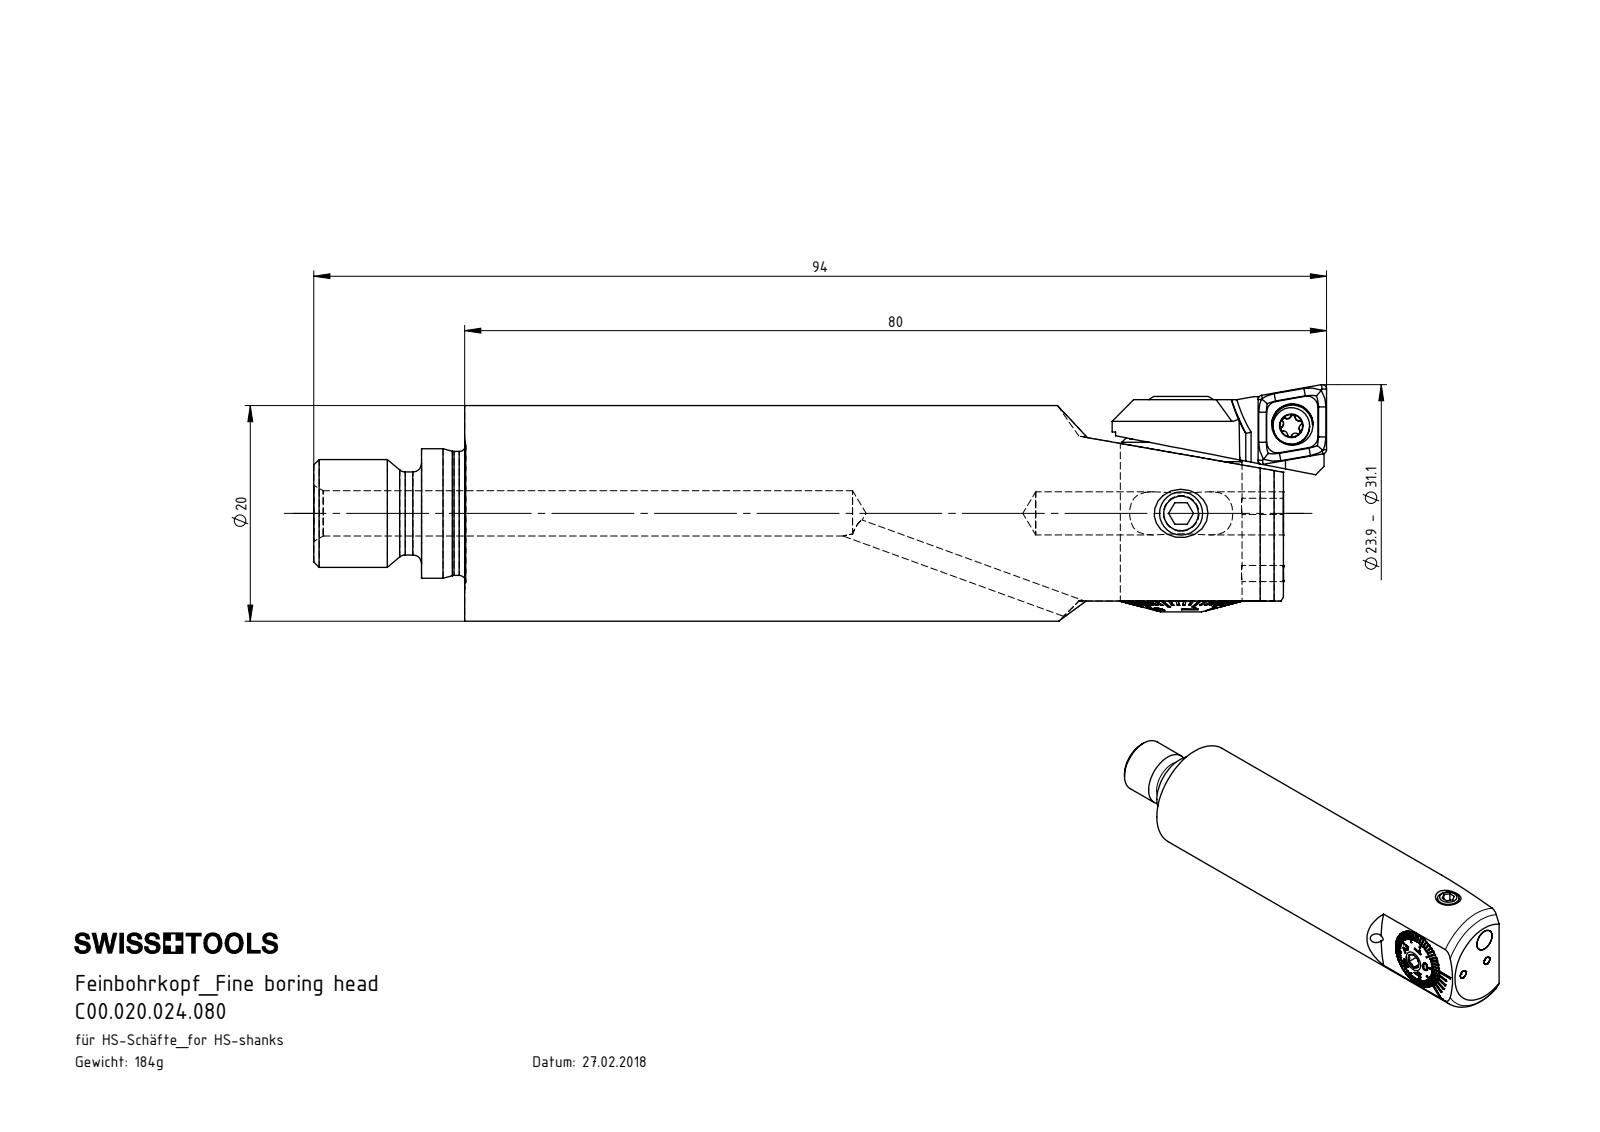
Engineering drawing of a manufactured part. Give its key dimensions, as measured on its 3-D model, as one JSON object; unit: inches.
{"part_name": "ISO 8744-1.5x5; ISO 4026 - M4 x 3; DIN 3771 - 9x1; C00.020.024.080 (+8 more)", "step_written_by": "SolidWorks 2017 (CONFIG_CONTROL_DESIGN)", "units": "inches", "bodies": {"solids": 15, "faces": 756, "planar": 336, "cylindrical": 142, "other": 278}, "overall_size": [3.701, 0.864, 0.787], "volume_in3": 1.433, "surface_area_in2": 15.85, "round_holes": [[0.055, 2], [0.13, 2], [0.02, 1], [0.059, 1], [0.079, 1], [0.081, 1], [0.11, 1], [0.148, 1], [0.152, 1], [0.157, 1], [0.165, 1], [0.177, 1]], "round_bosses_or_shafts": [[0.059, 3], [0.157, 2], [0.787, 1], [0.472, 1], [0.453, 1], [0.445, 1], [0.394, 1], [0.356, 1]], "partial_cylinders_radius": [[0.008, 6], [0.014, 5], [0.012, 2], [0.02, 2], [0.039, 2], [0.197, 2], [0.014, 1], [0.148, 1]], "face_to_face_distances": [2.992, 0.592, 0.039, 0.439, 0.153, 0.031, 0.11, 0.606, 0.551, 0.56], "hole_center_spacings": [0.03, 0.197, 0.22, 0.295]}
